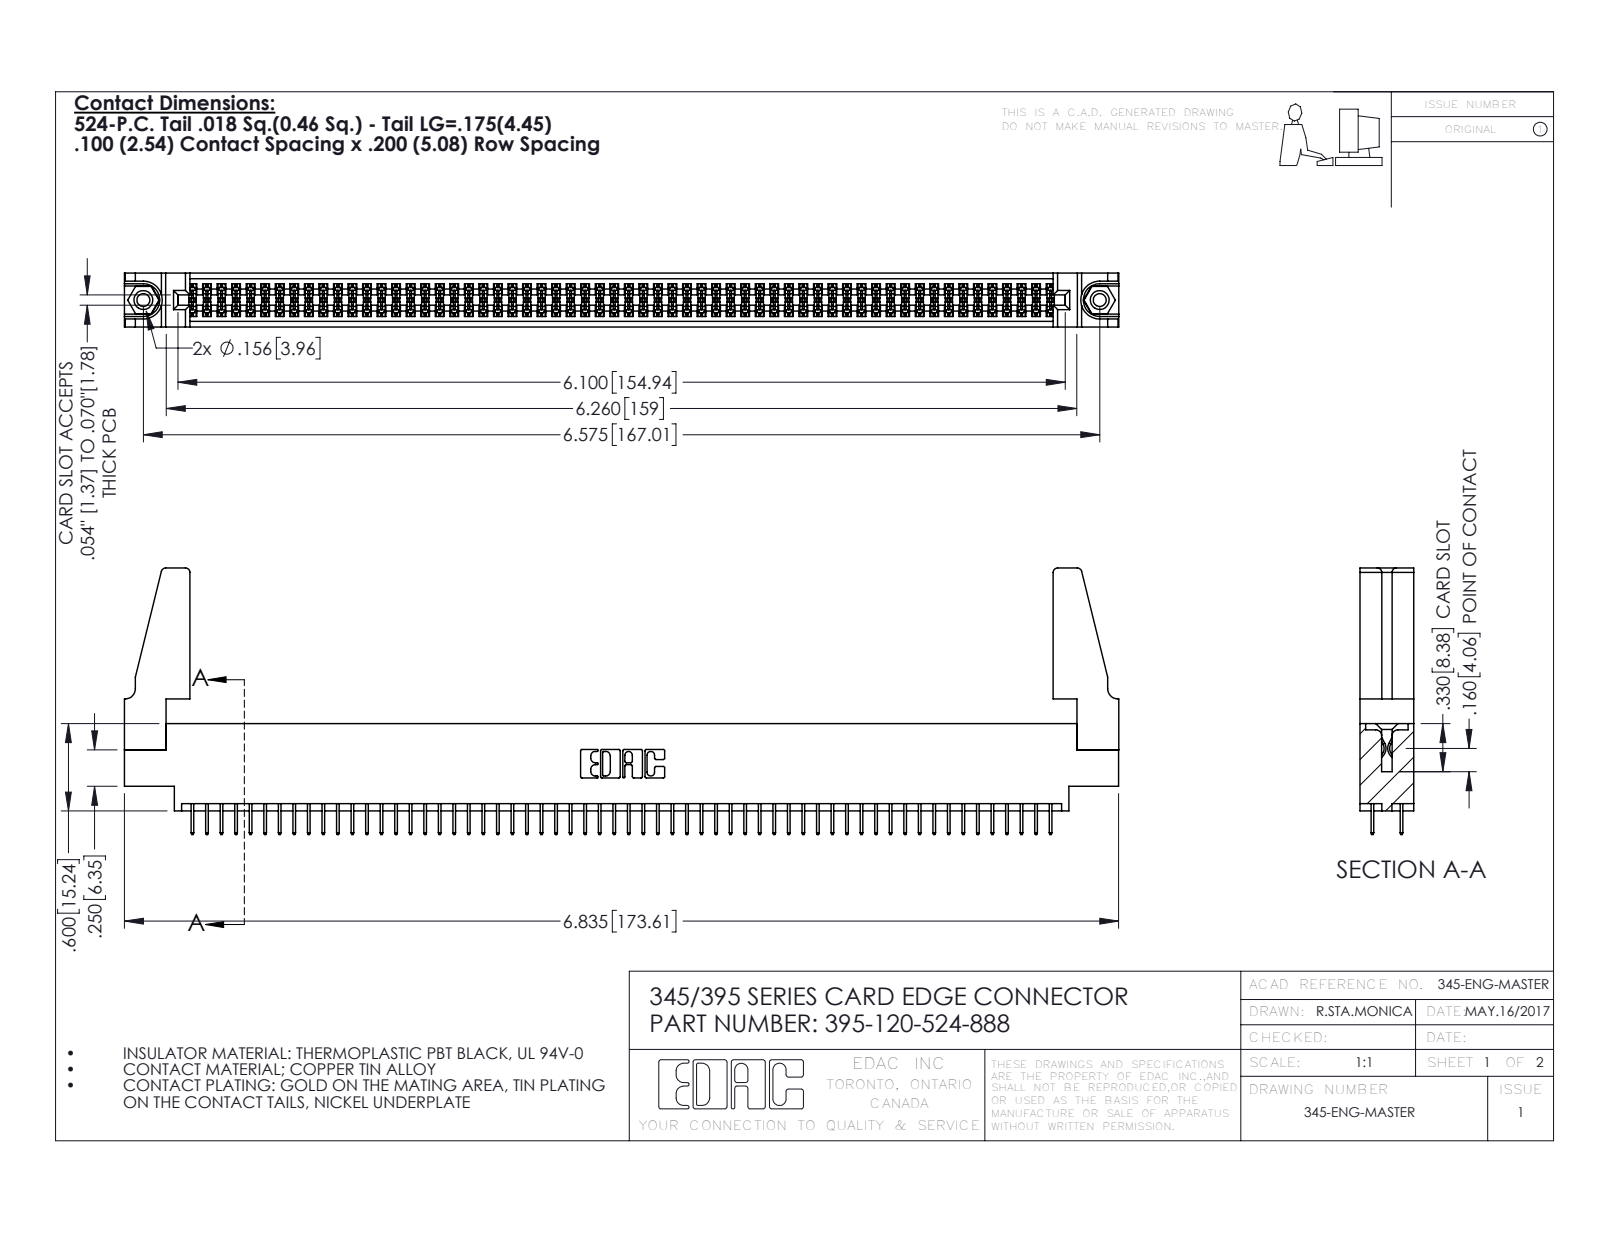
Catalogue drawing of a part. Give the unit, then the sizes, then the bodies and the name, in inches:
Units: inches
Overall size (bounding box): 6.836 × 1.832 × 0.37
Round holes (diameter × count): ⌀0.089 ×2, ⌀0.125 ×2, ⌀0.156 ×2, ⌀0.064 ×1
Round bosses / shafts (diameter × count): ⌀0.155 ×2
Partial cylindrical surfaces — rounded edges, fillets, slot ends (radius × count): R0.006 ×180, R0.01 ×22, R0.03 ×8, R0.007 ×6, R0.031 ×6, R0.026 ×3, R0.014 ×2, R0.019 ×2
Main face-to-face distances: 0.072, 0.298, 0.37, 0.2, 0.098, 0.272, 0.025, 0.225, 0.072, 0.175
Hole centre spacings: 0.27, 6.339, 6.575
Volume: 1.22 in³ · Surface area: 43.21 in²
Bodies: 125 solids, 6734 faces (4836 planar, 1882 cylindrical, 16 other)
Part name (STEP PRODUCT): 345 Part_0.170 Offset - 0.156 Dia-TH; 345-292-001_345-293-124; 345-220-078_345-220-088; 395-120-524-888 (+1 more)
STEP written by: SolidWorks 2016 (CONFIG_CONTROL_DESIGN)
